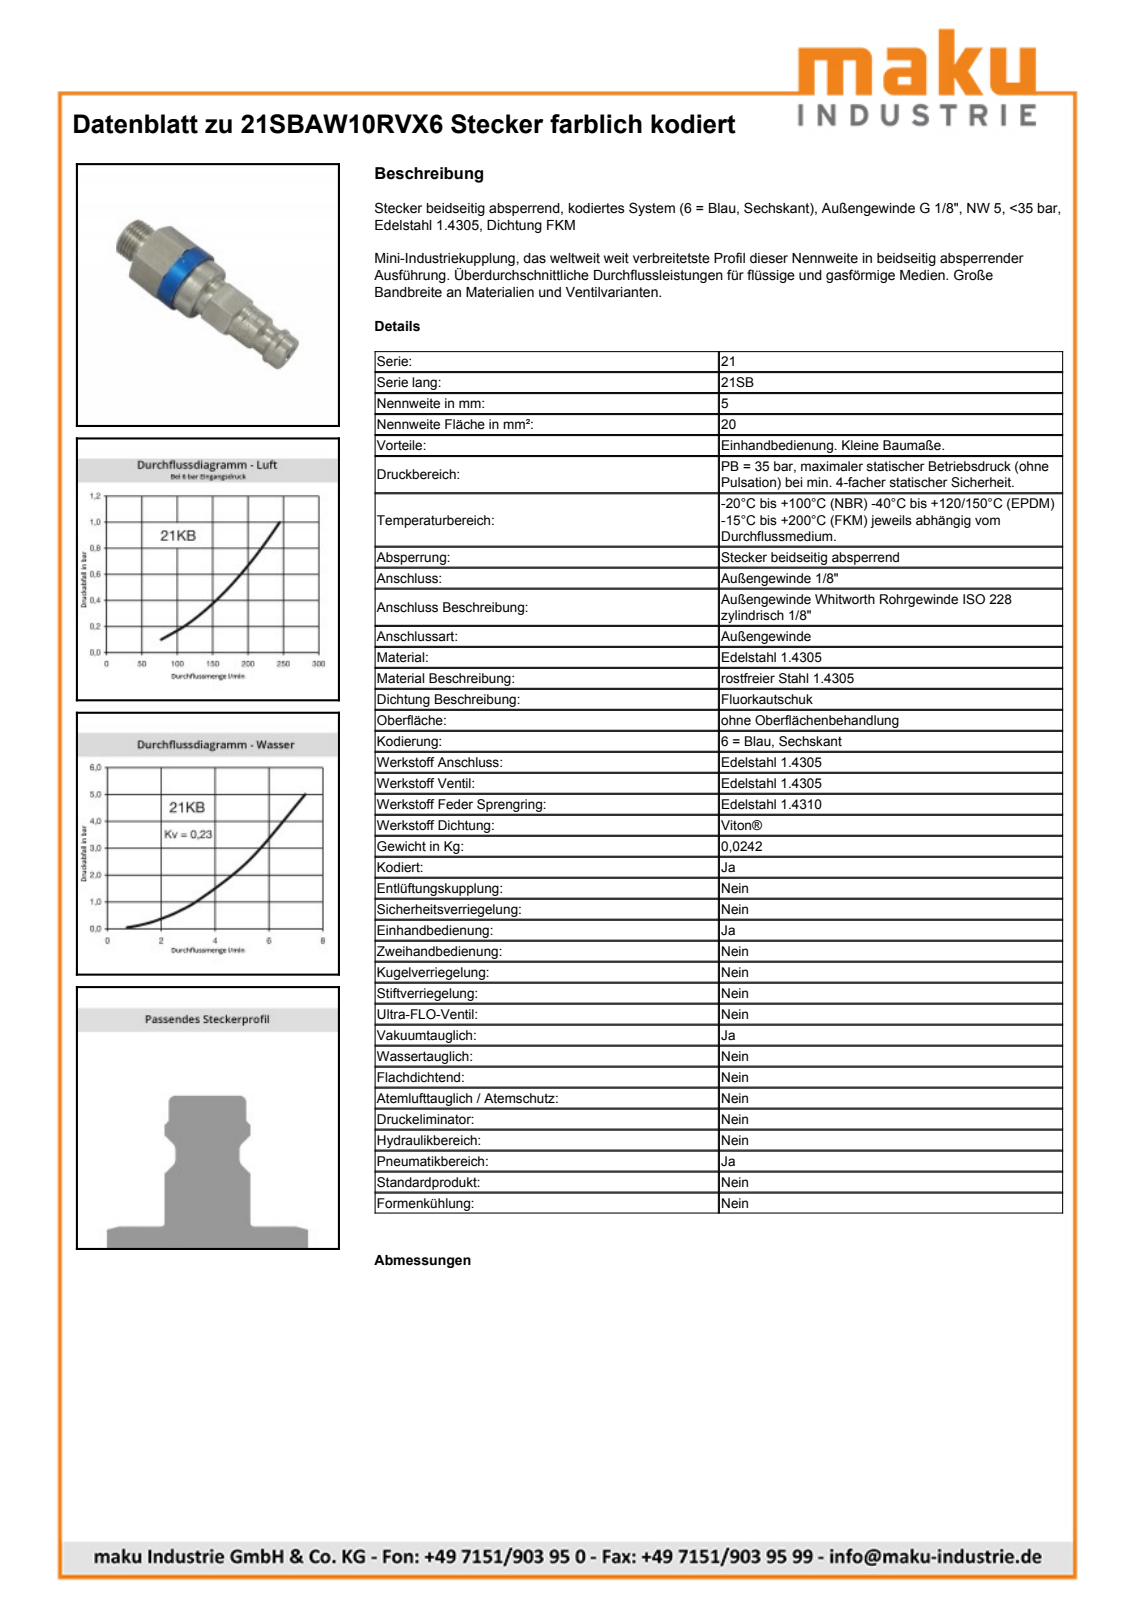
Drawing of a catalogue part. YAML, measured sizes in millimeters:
step_written_by: "Autodesk Inventor 2017 (AUTOMOTIVE_DESIGN)"
units: millimeters
bodies: {solids: 1, faces: 274, planar: 75, cylindrical: 49, other: 150}
overall_size: [48, 15.8, 15.5]
volume: 4124
surface_area: 4000
round_holes:
  - {diameter: 7.2, count: 1}
  - {diameter: 9.5, count: 1}
  - {diameter: 10.45, count: 1}
  - {diameter: 12, count: 1}
  - {diameter: 14.05, count: 1}
round_bosses_or_shafts:
  - {diameter: 15.5, count: 1}
  - {diameter: 14, count: 1}
  - {diameter: 10.85, count: 1}
  - {diameter: 9.73, count: 1}
  - {diameter: 9.7, count: 1}
  - {diameter: 9, count: 1}
  - {diameter: 8.5, count: 1}
  - {diameter: 8.1, count: 1}
partial_cylinders:
  - {radius: 4.15, count: 1}
  - {radius: 5.7, count: 1}
  - {radius: 7.9, count: 1}
face_to_face_distances: [14, 10, 7, 9, 2, 4.75, 24.5, 17.5, 15.5, 48]
